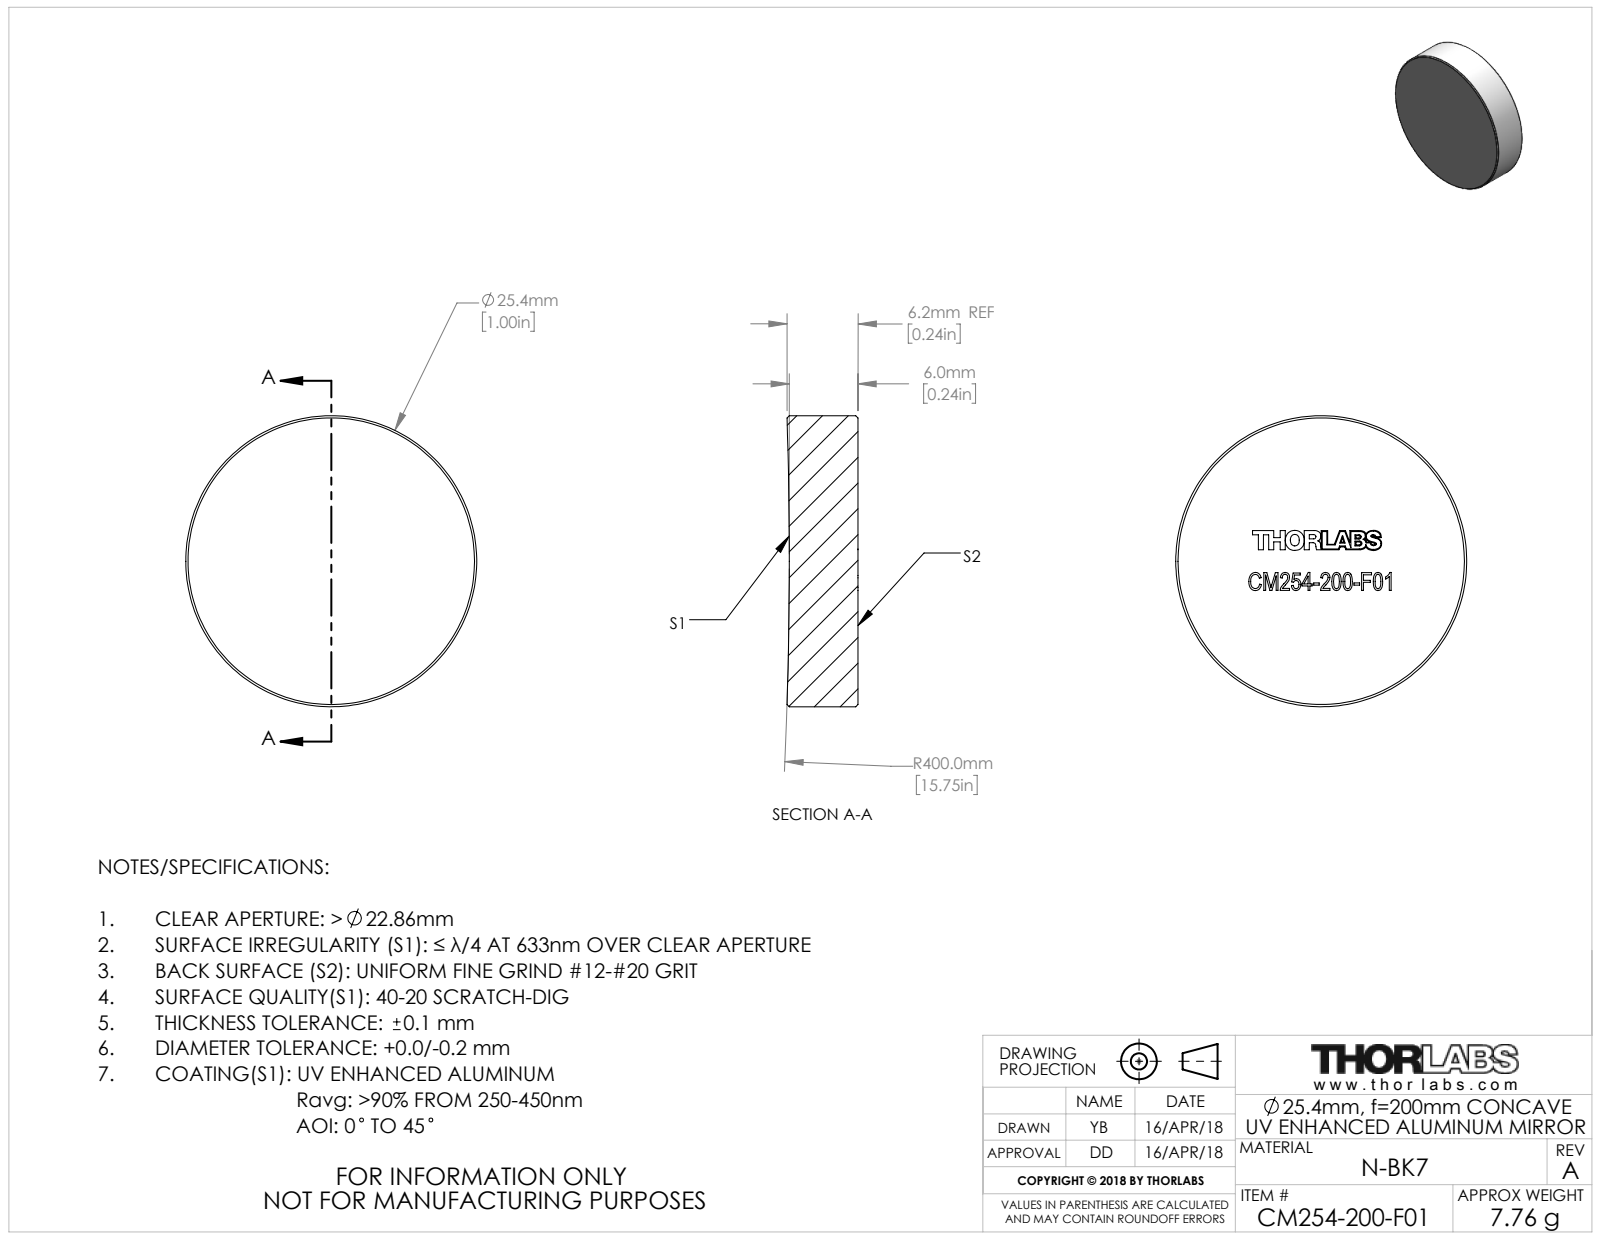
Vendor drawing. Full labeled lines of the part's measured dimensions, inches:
Part name (STEP PRODUCT): TTN153281-E0W
STEP written by: SolidWorks 2018 (CONFIG_CONTROL_DESIGN)
Units: inches
Bodies: 1 solid, 41 faces (33 planar, 2 cylindrical, 6 other)
Overall size (bounding box): 1 × 1 × 0.244
Volume: 0.188 in³ · Surface area: 2.308 in²
Round bosses / shafts (diameter × count): ⌀1 ×1
